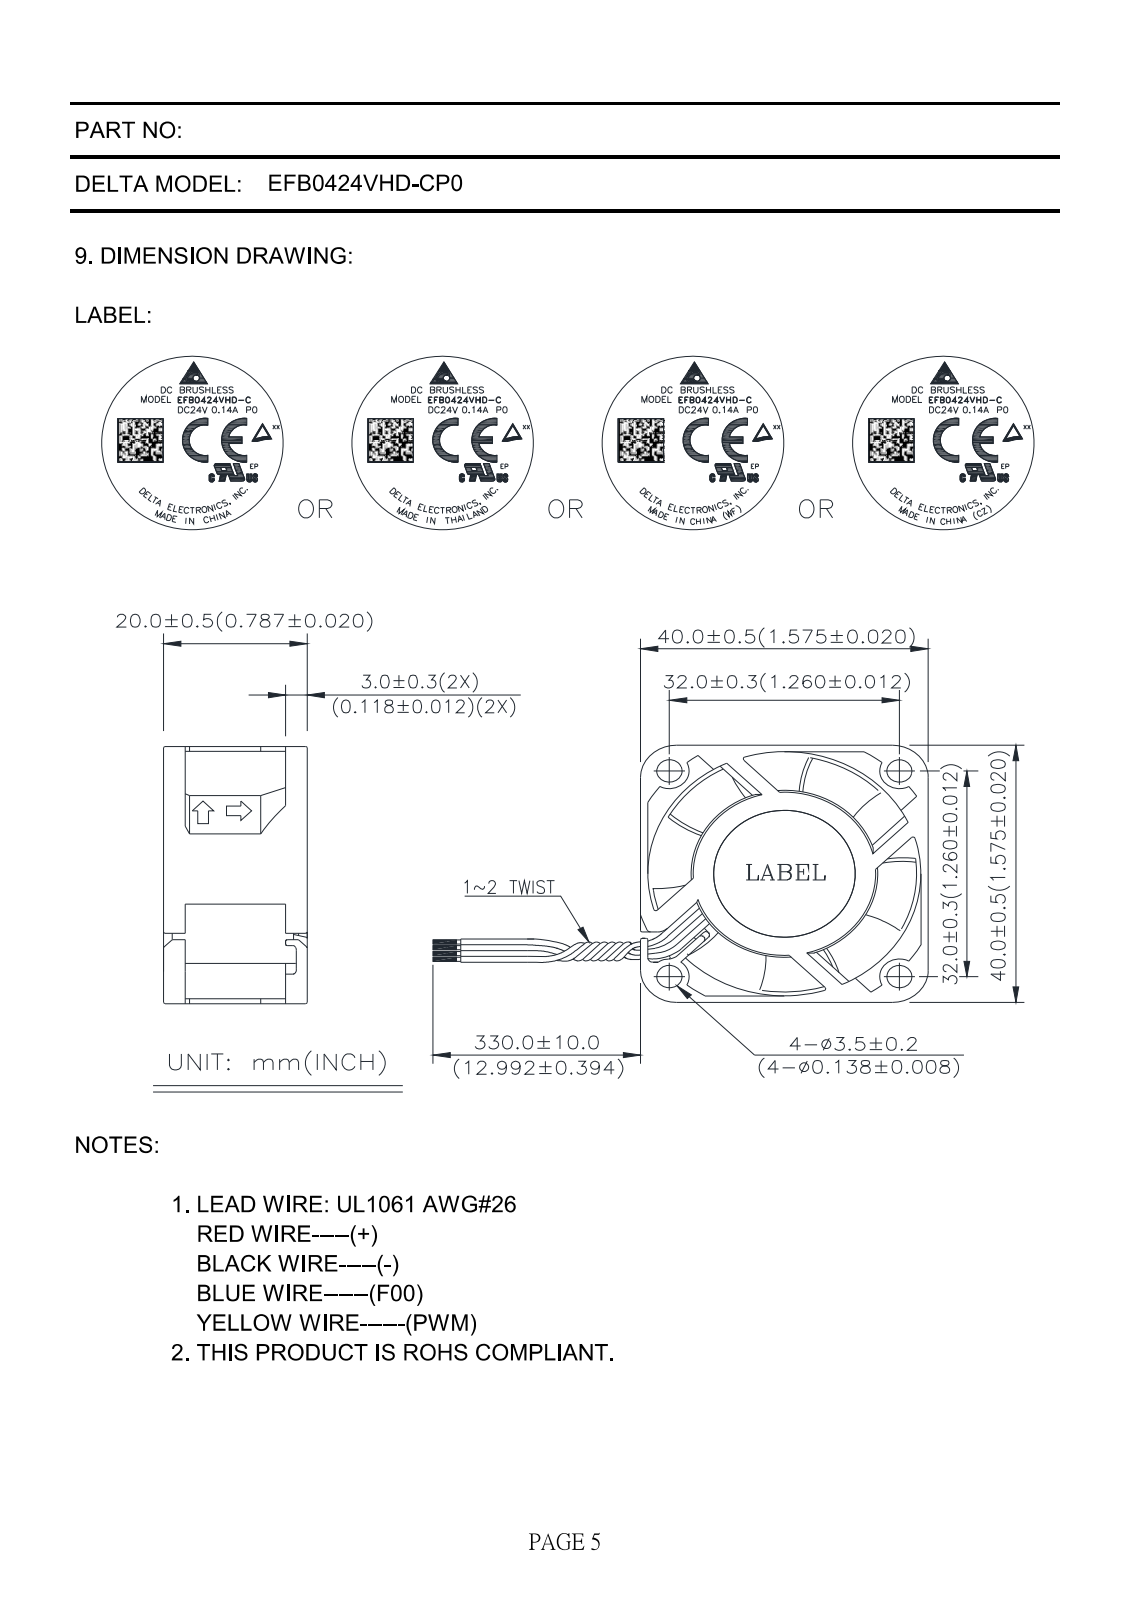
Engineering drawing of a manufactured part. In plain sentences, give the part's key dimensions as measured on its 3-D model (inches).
The part is named "4102113800". Its 3-D file was written by "CREO PARAMETRIC BY PTC INC, 2015080 (AUTOMOTIVE_DESIGN)". It is 1 solid with 316 faces: 217 planar, 66 cylindrical and 33 other. Overall it measures 1.575 by 1.575 by 0.787 inches. Its volume is 1.521 cubic inches and its surface area 14 square inches. Round holes: 4 of diameter 0.138, 1 of diameter 1.496. Round bosses or shafts: 1 of diameter 1.024. Partial cylindrical surfaces (rounded edges, fillets, slot ends): 4 of radius 0.012, 4 of radius 0.108, 4 of radius 0.128, 4 of radius 0.197, 3 of radius 0.039, 1 of radius 0.028, 1 of radius 0.079, 1 of radius 0.807. The main face-to-face distances are 0.679, 1.575, 0.02, 0.659, 0.039, 1.535, 0.108, 0.787, 0.768, 0.118. The hole center spacings are 0.891, 1.26, 1.781.
